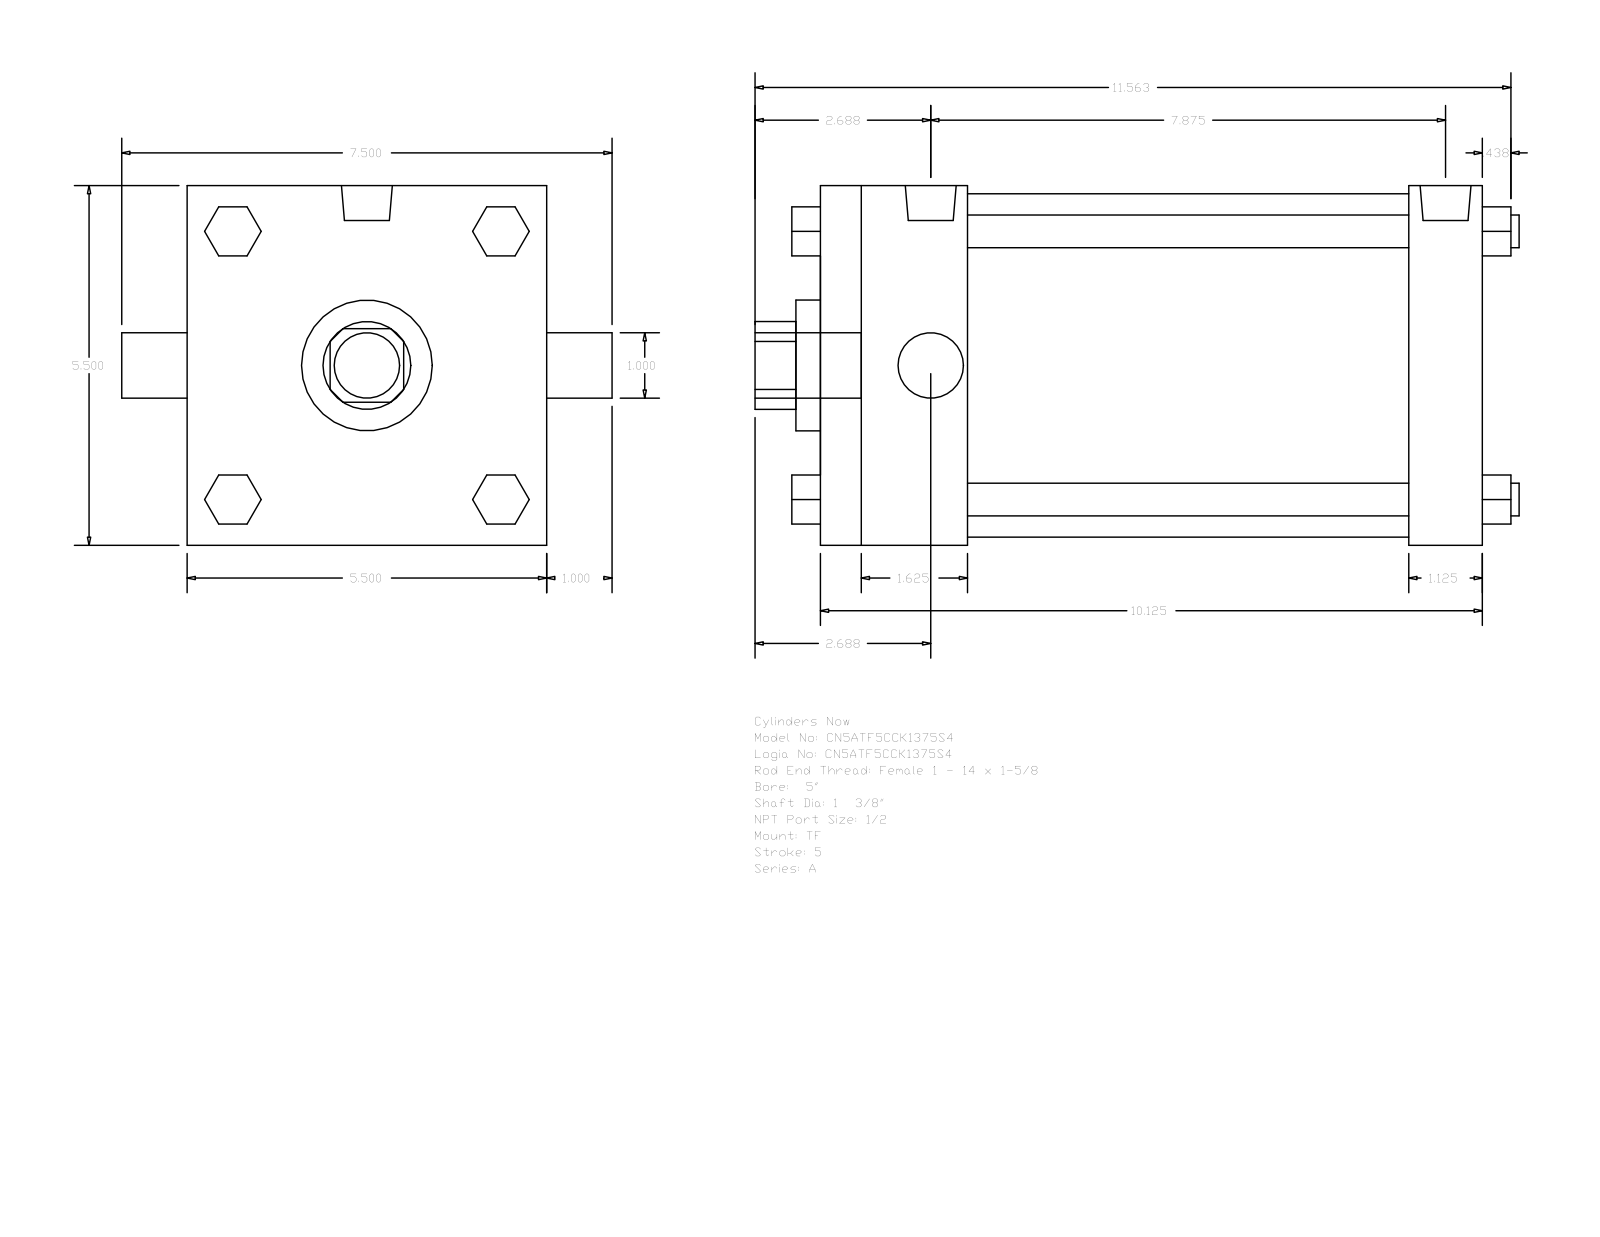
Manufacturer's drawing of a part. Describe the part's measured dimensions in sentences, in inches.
The part is named "A_TF__0500_1.375". Its 3-D file was written by "GSSL Pune (CONFIG_CONTROL_DESIGN)". It is 0 solids with 120 faces: 92 planar, 28 cylindrical and 0 other. Overall it measures 11.687 by 7.5 by 5.5 inches. Round holes: 1 of diameter 1, 1 of diameter 1.375, 1 of diameter 2, 1 of diameter 5.25. Round bosses or shafts: 4 of diameter 0.5, 3 of diameter 0.344, 2 of diameter 0.778, 1 of diameter 1. Partial cylindrical surfaces (rounded edges, fillets, slot ends): 1 of radius 0.672. The main face-to-face distances are 5.5, 10.125, 1.125, 9, 2.25, 6.75, 7.875, 0.75, 2.05, 3.55.
